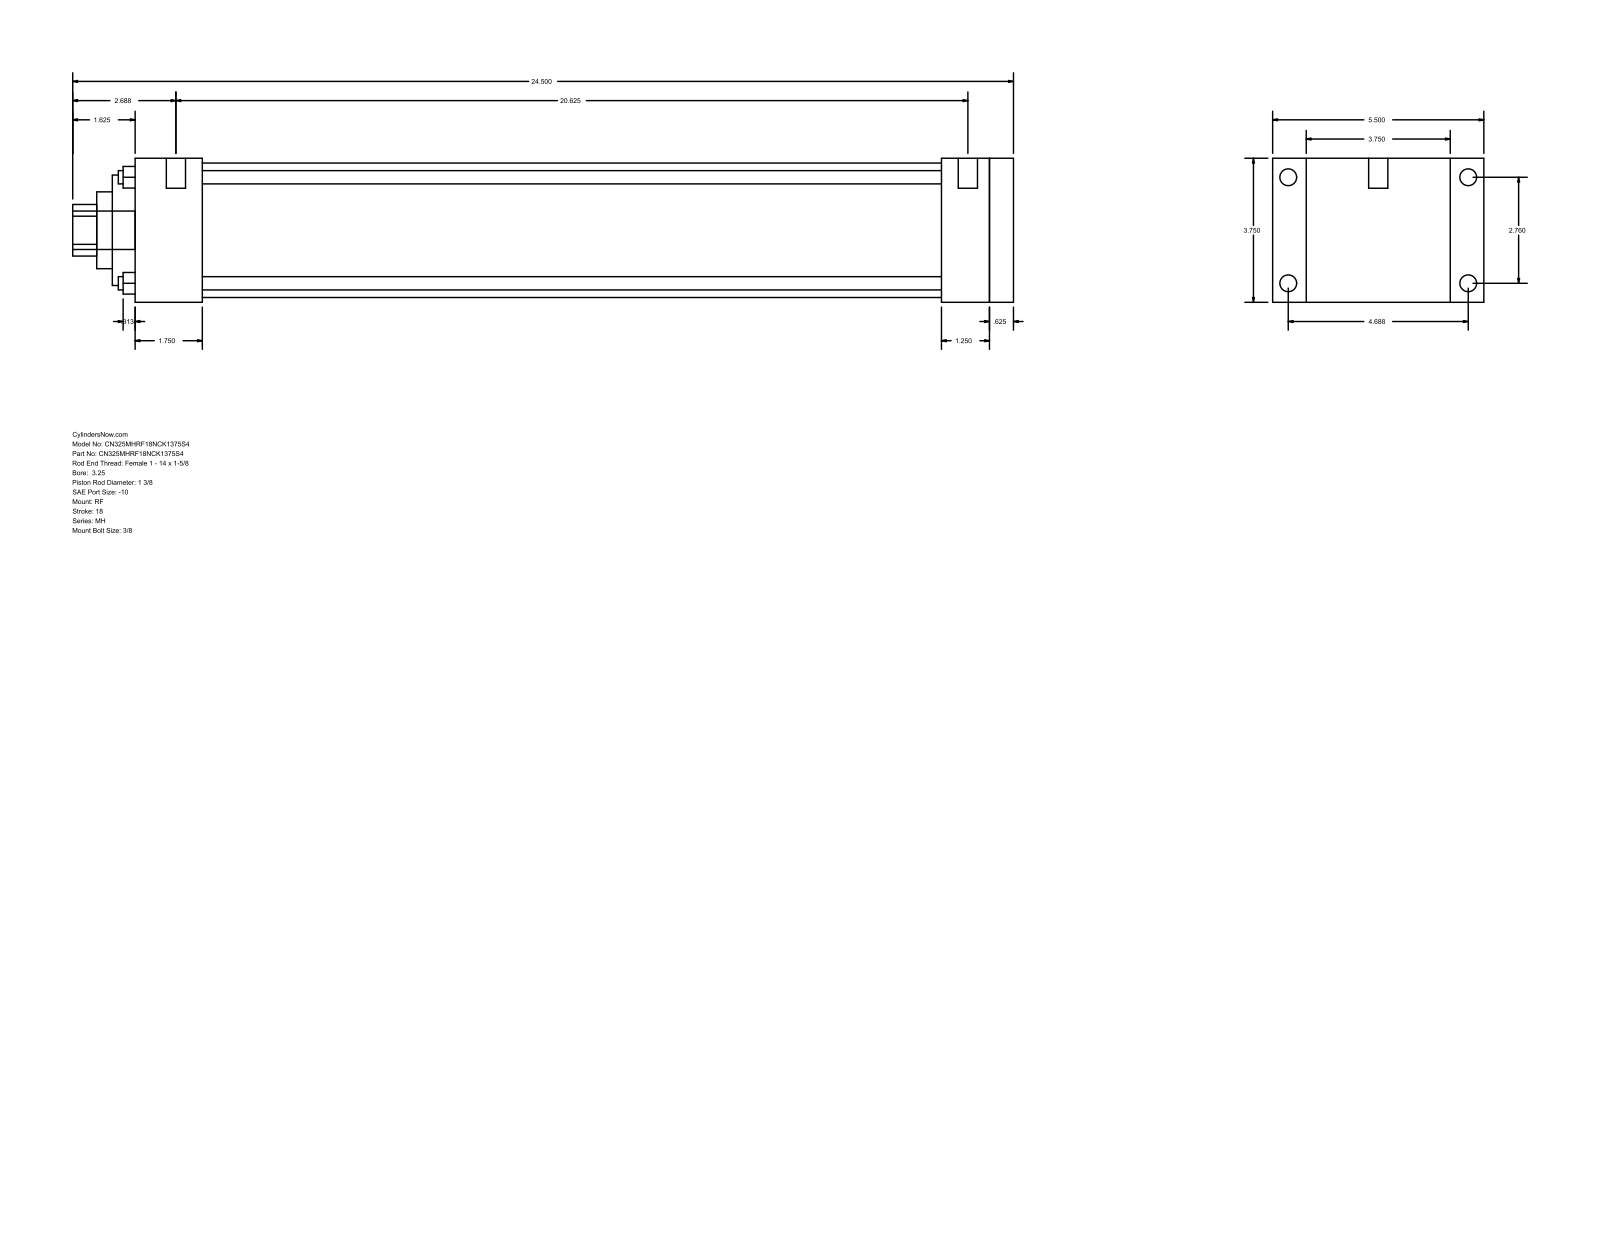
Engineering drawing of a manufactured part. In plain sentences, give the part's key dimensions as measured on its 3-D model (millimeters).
The part is named "MH_RF__0325_1.375". Its 3-D file was written by "GSSL Pune (CONFIG_CONTROL_DESIGN)". It is 0 solids with 94 faces: 65 planar, 29 cylindrical and 0 other. Overall it measures 622.3 by 139.7 by 95.25 millimeters. Round holes: 4 of diameter 8.76, 1 of diameter 34.92, 1 of diameter 50.8, 1 of diameter 73.03, 1 of diameter 88.9. Round bosses or shafts: 4 of diameter 11.13, 4 of diameter 5.56, 2 of diameter 12.7, 1 of diameter 25.4. Partial cylindrical surfaces (rounded edges, fillets, slot ends): 1 of radius 17.06. The main face-to-face distances are 95.24, 581.03, 15.88, 565.15, 22.23, 117.47, 44.45, 520.7, 536.58, 533.4. The hole center spacings are 49.57, 70.1, 99.14.
